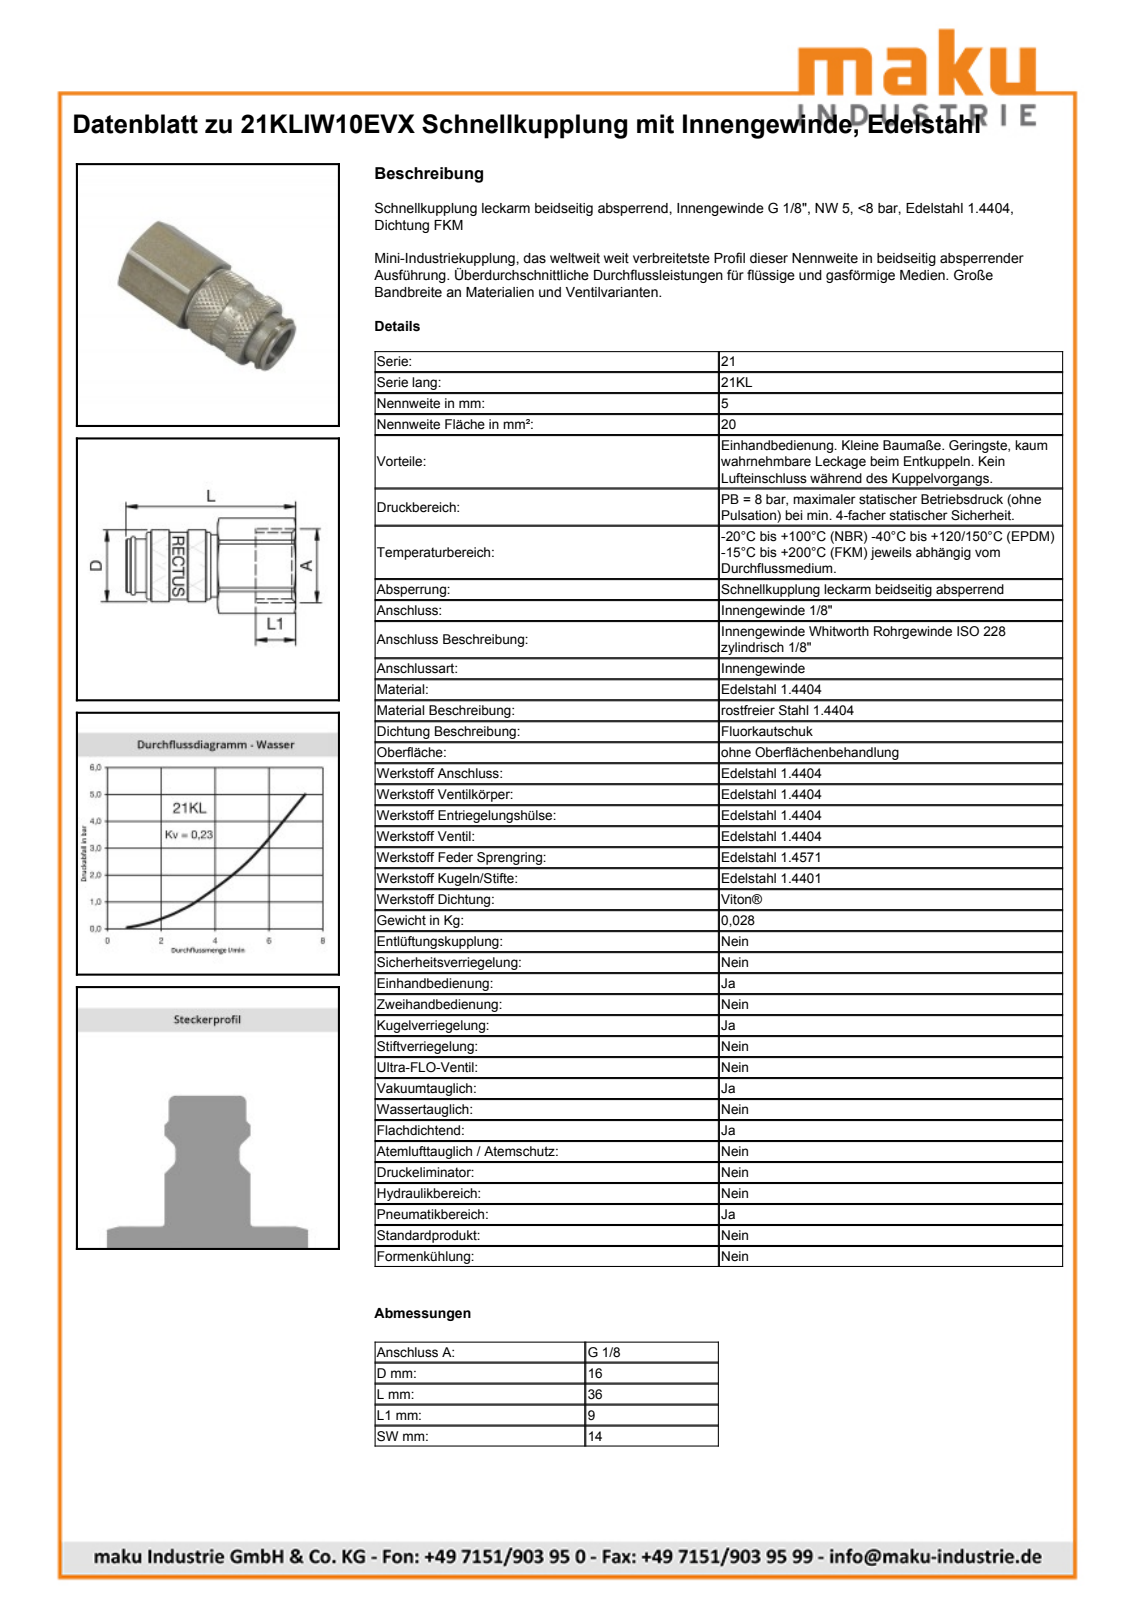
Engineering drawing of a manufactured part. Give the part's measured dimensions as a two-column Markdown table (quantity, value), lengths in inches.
| quantity | value |
| --- | --- |
| part name | D109505 |
| STEP written by | Autodesk Inventor 2013 (AUTOMOTIVE_DESIGN) |
| units | inches |
| bodies | 2 solids, 388 faces (129 planar, 60 cylindrical, 199 other) |
| overall size | 1.423 × 0.636 × 0.636 |
| volume | 0.328 in³ |
| surface area | 5.791 in² |
| round holes (diameter × count) | 0.337 × 1, 0.478 × 1, 0.551 × 1 |
| round bosses / shafts (diameter × count) | 0.636 × 1, 0.594 × 1, 0.472 × 1, 0.449 × 1, 0.439 × 1 |
| partial cylindrical surfaces (radius × count) | 0.219 × 1, 0.293 × 1, 0.311 × 1 |
| main face-to-face distances | 0.551, 1.423, 1.093, 0.331, 0.181, 0.911, 1.242, 0.469, 0.287, 0.624 |
